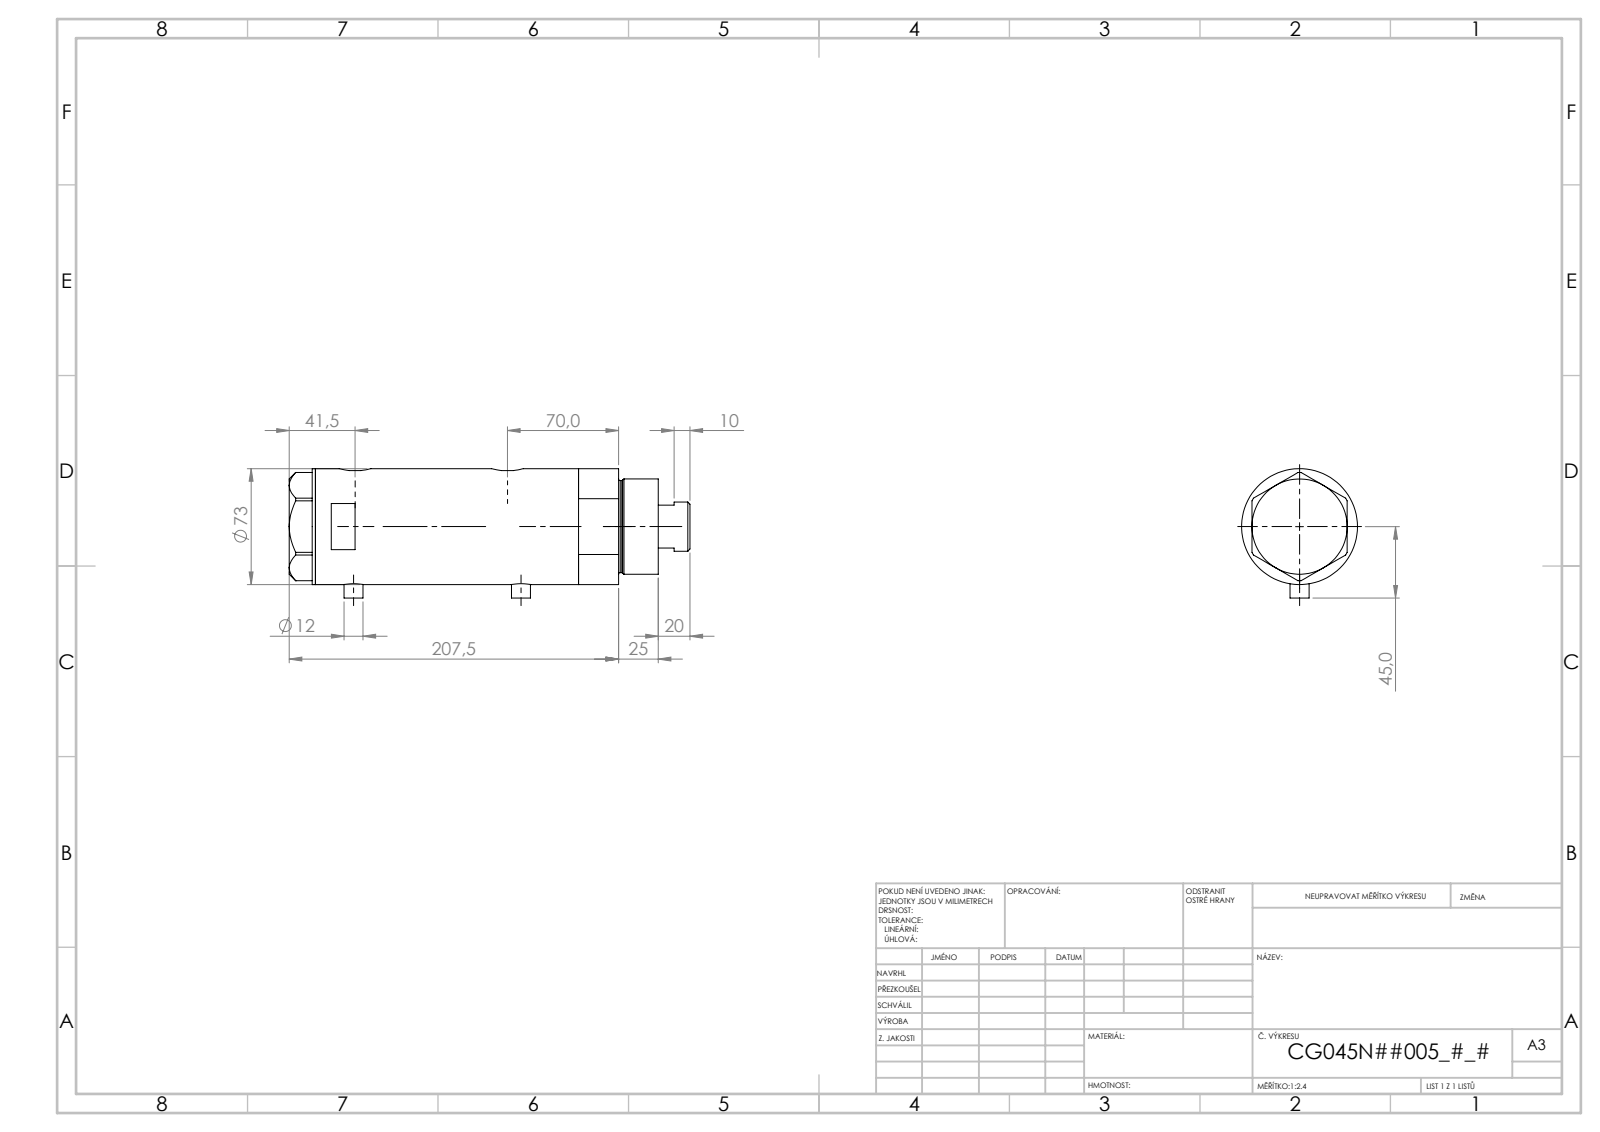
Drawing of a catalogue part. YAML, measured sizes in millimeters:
part_name: "V270CG_VC; V270CG_FRONT; V270CG_MIDDLE; V270CG_BACK"
step_written_by: "SolidWorks 2019 (CONFIG_CONTROL_DESIGN)"
units: millimeters
bodies: {solids: 4, faces: 125, planar: 50, cylindrical: 55, other: 20}
overall_size: [196.52, 74.1, 73]
volume: 683752
surface_area: 122297
round_holes:
  - {diameter: 5, count: 2}
  - {diameter: 12.5, count: 2}
  - {diameter: 13.16, count: 2}
  - {diameter: 10.5, count: 1}
  - {diameter: 32, count: 1}
  - {diameter: 33.5, count: 1}
  - {diameter: 45, count: 1}
  - {diameter: 48, count: 1}
  - {diameter: 64, count: 1}
round_bosses_or_shafts:
  - {diameter: 12, count: 2}
  - {diameter: 73, count: 1}
  - {diameter: 60, count: 1}
  - {diameter: 58, count: 1}
  - {diameter: 31, count: 1}
partial_cylinders:
  - {radius: 10, count: 2}
face_to_face_distances: [26, 16.49, 42.49, 88.65, 72.16, 46.16, 160.03, 176.52, 134.03, 87.87]
hole_center_spacings: [56.65, 0.99, 1, 8.5, 8.51, 47.15, 48.14, 48.15]
